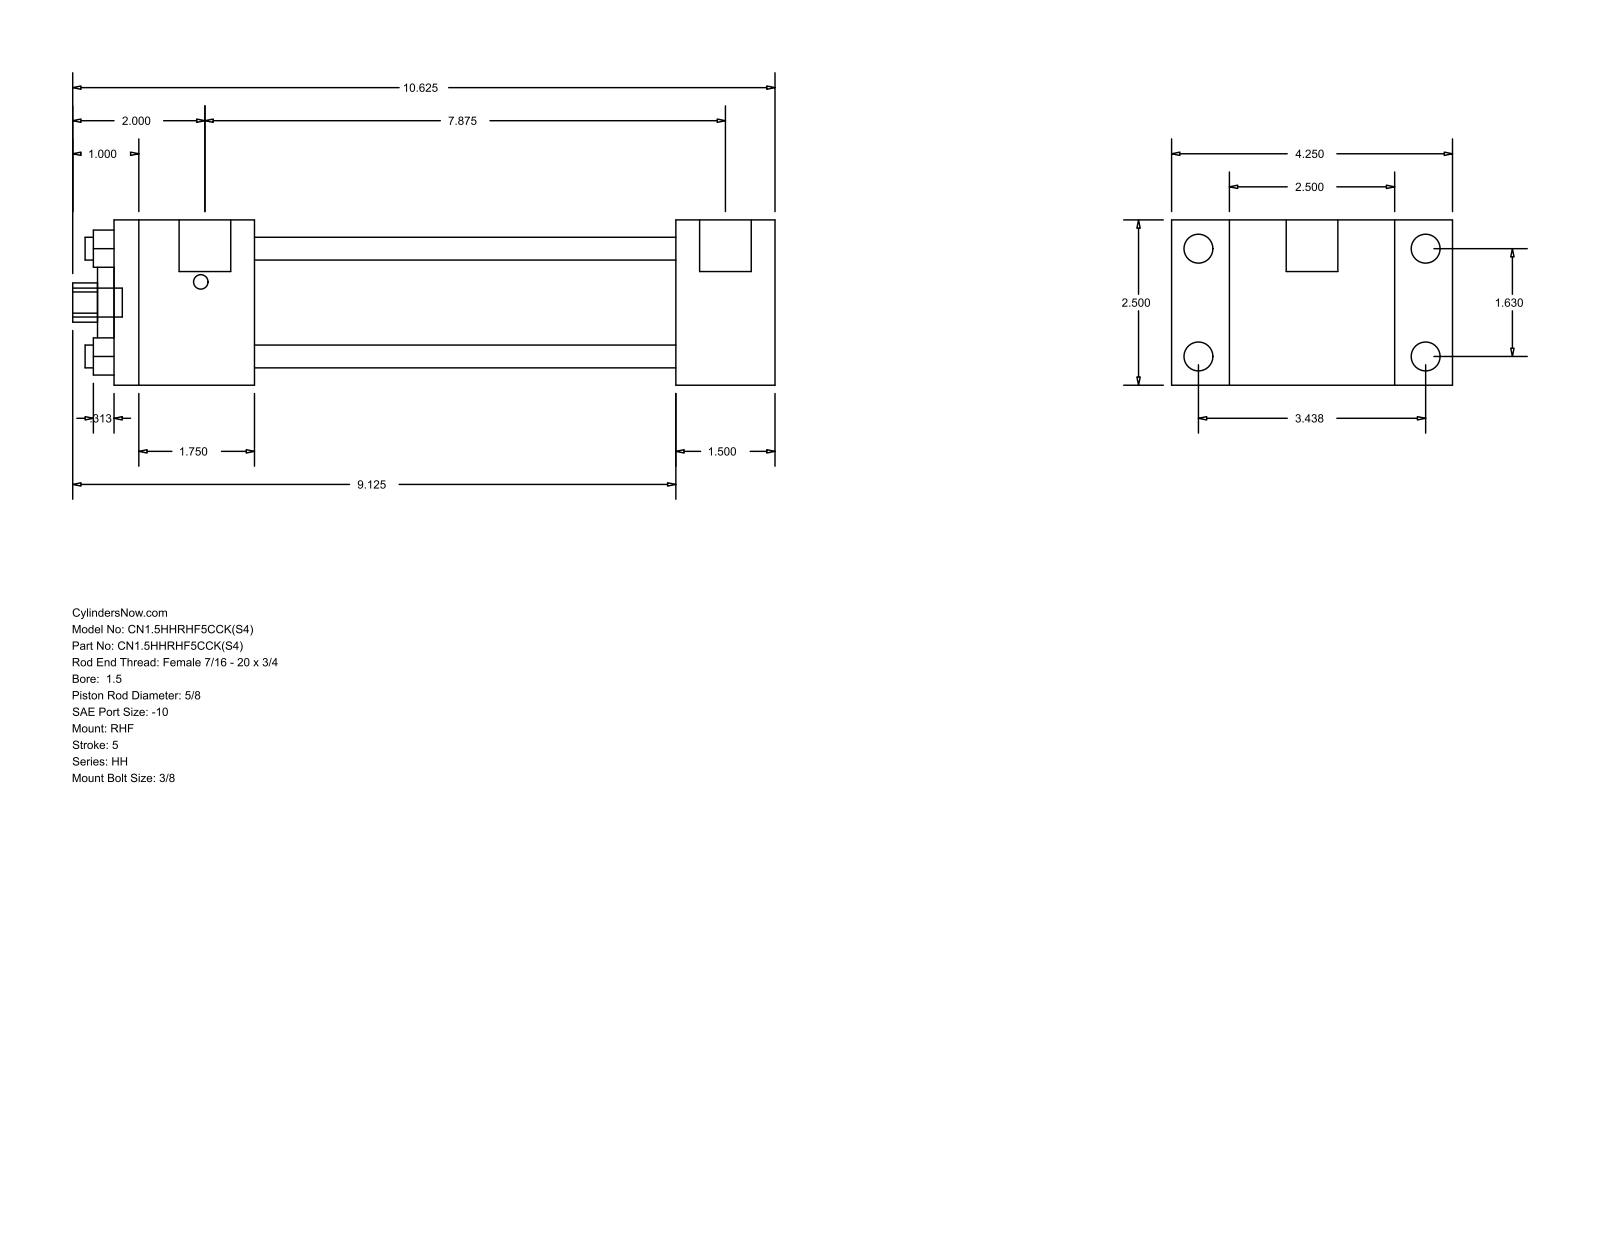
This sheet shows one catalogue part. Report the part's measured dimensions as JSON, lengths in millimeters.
{"part_name": "HH_RHF__0150_0.625", "step_written_by": "GSSL Pune (CONFIG_CONTROL_DESIGN)", "units": "millimeters", "bodies": {"solids": 0, "faces": 88, "planar": 60, "cylindrical": 28, "other": 0}, "overall_size": [269.88, 107.95, 63.5], "round_holes": [[8.76, 4], [15.88, 1], [28.57, 1], [44.45, 1]], "round_bosses_or_shafts": [[11.13, 4], [5.56, 4], [19.84, 2], [11.11, 1]], "partial_cylinders_radius": [[7.54, 1]], "face_to_face_distances": [63.5, 38.1, 22.23, 85.73, 215.9, 254, 107.96, 53.97, 161.93, 200.03], "hole_center_spacings": [29.27, 41.4, 58.55]}
